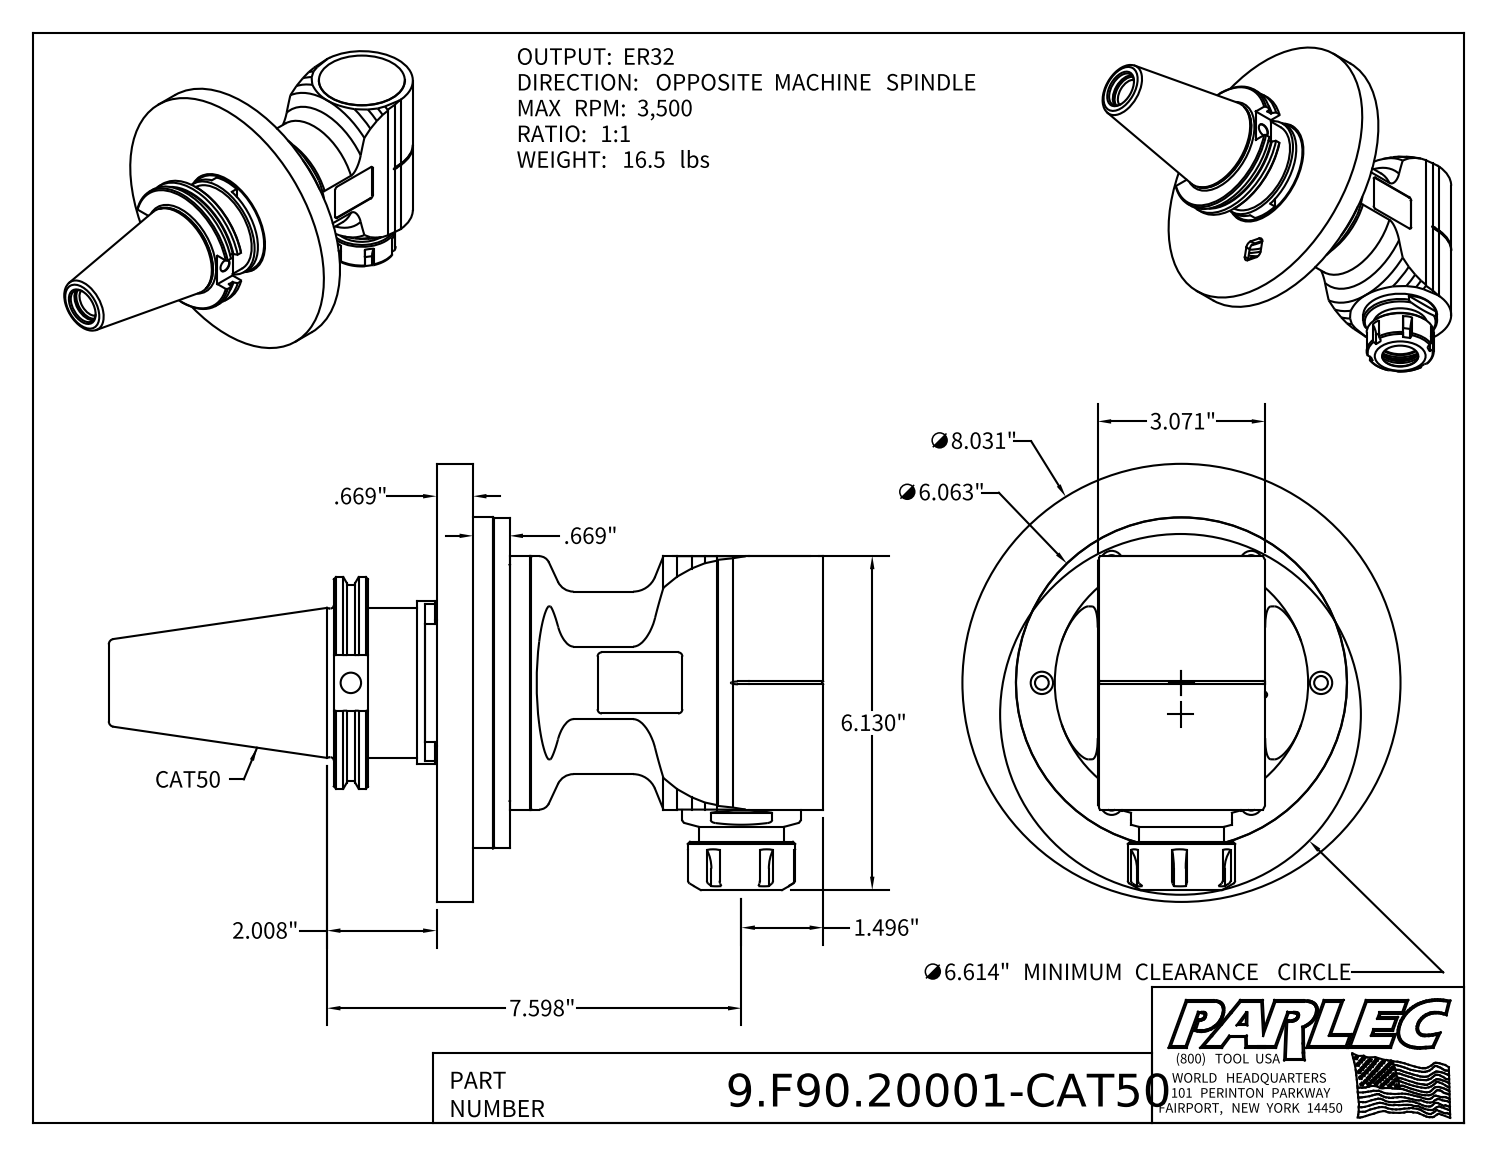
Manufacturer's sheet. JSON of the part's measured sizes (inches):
{"part_name": "9.F90.20001-CAT50; 9_SK_45_2 (Cat50, MTC); 9_FL_F90T2 (MTC, Universal Flange, Type 2); 9_F90_20001", "step_written_by": "Autodesk Inventor 2022 (AUTOMOTIVE_DESIGN)", "units": "inches", "bodies": {"solids": 7, "faces": 402, "planar": 194, "cylindrical": 104, "other": 104}, "overall_size": [13.094, 8.031, 8.031], "volume_in3": 146.4, "surface_area_in2": 460.2, "round_holes": [[0.409, 10], [0.252, 6], [0.375, 1], [0.492, 1], [0.787, 1], [0.865, 1], [0.945, 1], [1.031, 1], [1.055, 1], [1.063, 1], [1.161, 1], [1.409, 1]], "round_bosses_or_shafts": [[0.394, 4], [0.236, 4], [0.098, 2], [8.031, 1], [6.071, 1], [6.063, 1], [4.78, 1], [4.646, 1]], "partial_cylinders_radius": [[0.079, 12], [0.157, 6], [0.591, 6], [0.016, 2], [1.496, 1], [1.673, 1]], "face_to_face_distances": [0.669, 1.339, 0.138, 0.531, 1.201, 0.02, 0.354, 0.886, 0.217, 1.555], "hole_center_spacings": [2.559, 0.857, 1.929, 2.559, 2.778, 3.581, 4.154, 4.433]}
